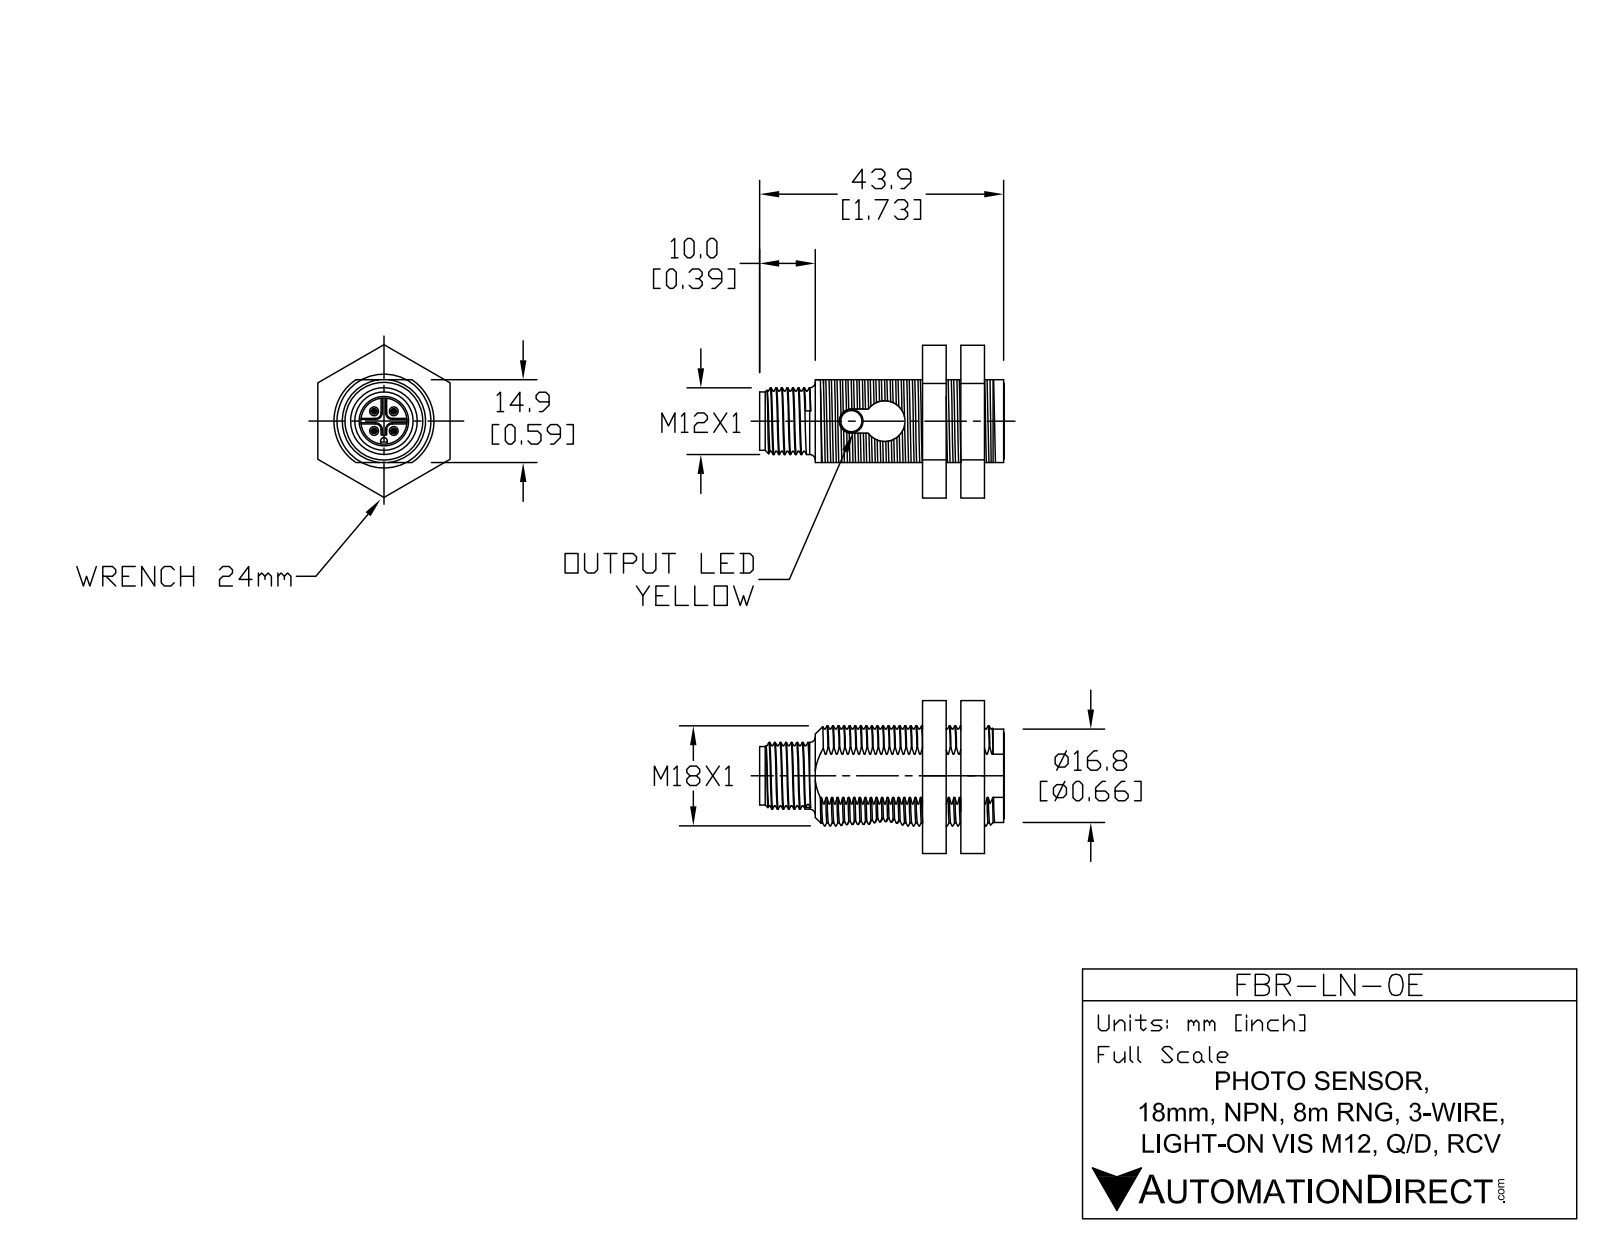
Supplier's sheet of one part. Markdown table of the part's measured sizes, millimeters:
| quantity | value |
| --- | --- |
| part name | FBR-LN-0E |
| STEP written by | SolidWorks 2017 (AUTOMOTIVE_DESIGN) |
| units | millimeters |
| bodies | 3 solids, 104 faces (35 planar, 27 cylindrical, 42 other) |
| overall size | 44 × 27.7 × 24 |
| volume | 10 500 mm³ |
| surface area | 5 054 mm² |
| round holes (diameter × count) | 7.3 × 1, 8.3 × 1, 16.9 × 1 |
| round bosses / shafts (diameter × count) | 12 × 1, 10.5 × 1, 4.2 × 1 |
| partial cylindrical surfaces (radius × count) | 1.1 × 4, 0.6 × 1, 2.2 × 1, 7.7 × 1, 8.4 × 1, 9 × 1 |
| main face-to-face distances | 24, 4, 14.9, 4.5, 19.5, 10, 8, 14, 6, 34 |
